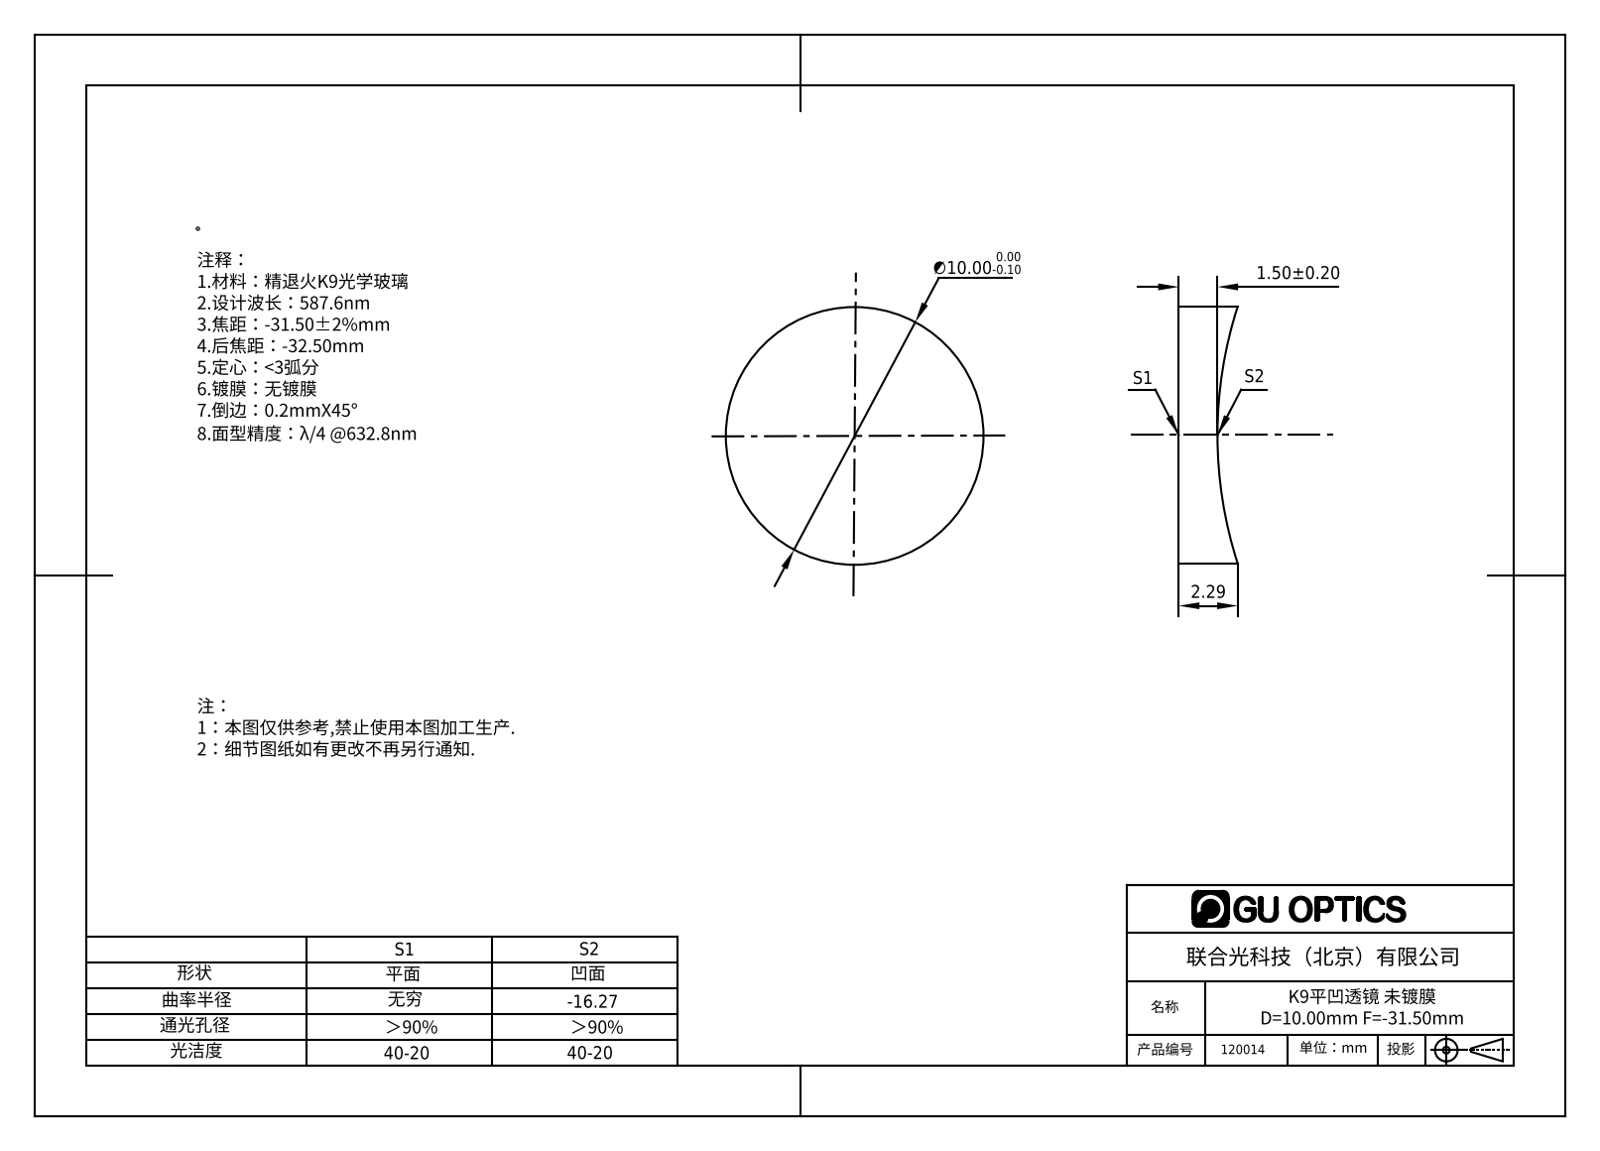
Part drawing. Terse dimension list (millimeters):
name: 120014
written by: SolidWorks 2016 (AUTOMOTIVE_DESIGN)
unit: mm
bodies: 1 solid, 5 faces (1 planar, 2 cylindrical, 2 other)
size: 10 × 10 × 2.29
volume: 149 mm³; area: 231 mm²
bosses: 1× ⌀10
